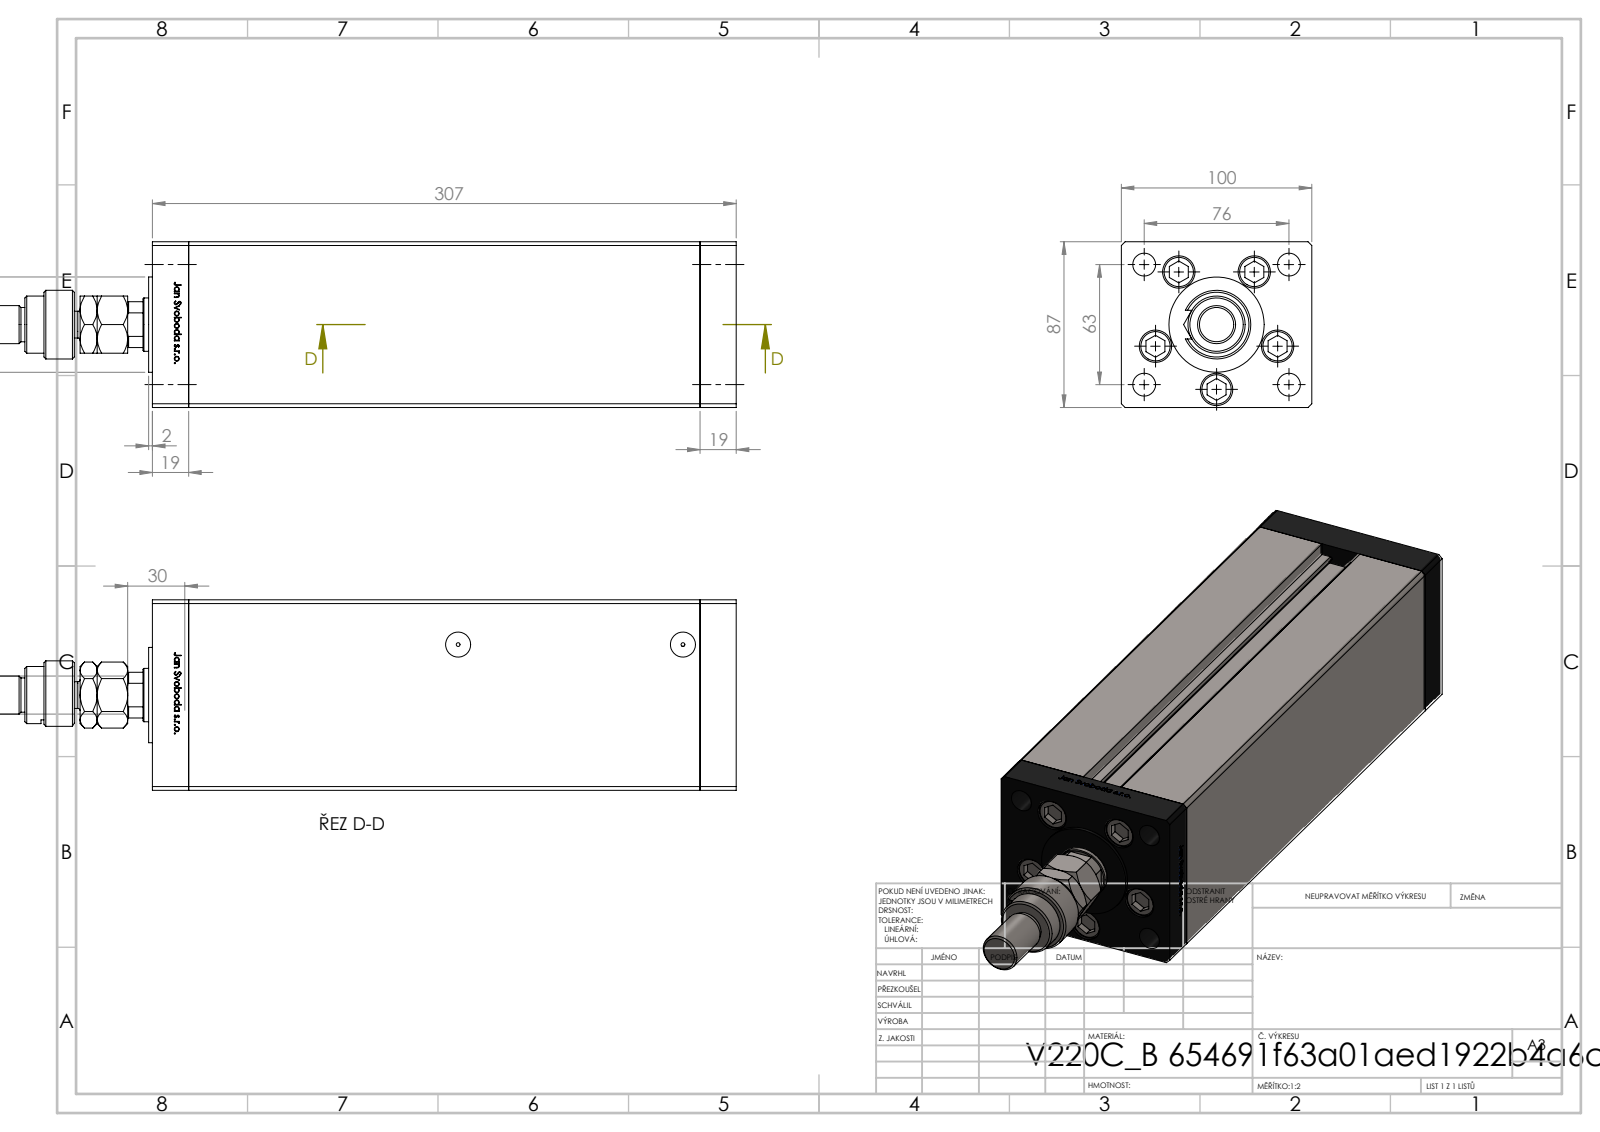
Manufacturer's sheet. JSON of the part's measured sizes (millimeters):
{"part_name": "V220C_VC_B; FEMALE_PART_FOR_DFA; MFA; V220C_FRONT_B (+3 more)", "step_written_by": "SolidWorks 2019 (CONFIG_CONTROL_DESIGN)", "units": "millimeters", "bodies": {"solids": 16, "faces": 1270, "planar": 492, "cylindrical": 160, "other": 618}, "overall_size": [403.5, 100, 87], "volume_mm3": 2339000, "surface_area_mm2": 295223, "round_holes": [[13.5, 7], [17, 5], [12, 4], [2, 2], [13.16, 2], [18.5, 1], [28, 1]], "round_bosses_or_shafts": [[8, 5], [17, 2], [50, 1], [36, 1], [30, 1], [22, 1], [20, 1], [18, 1]], "partial_cylinders_radius": [[0.93, 2], [7.5, 1], [12, 1], [13.5, 1]], "face_to_face_distances": [100, 87, 19, 268.5, 287.5, 34.25, 306.5, 15.25, 253.25, 272.25], "hole_center_spacings": [34, 18.59, 39.64, 49.36, 57.95, 21.03, 38.08, 39.27]}
